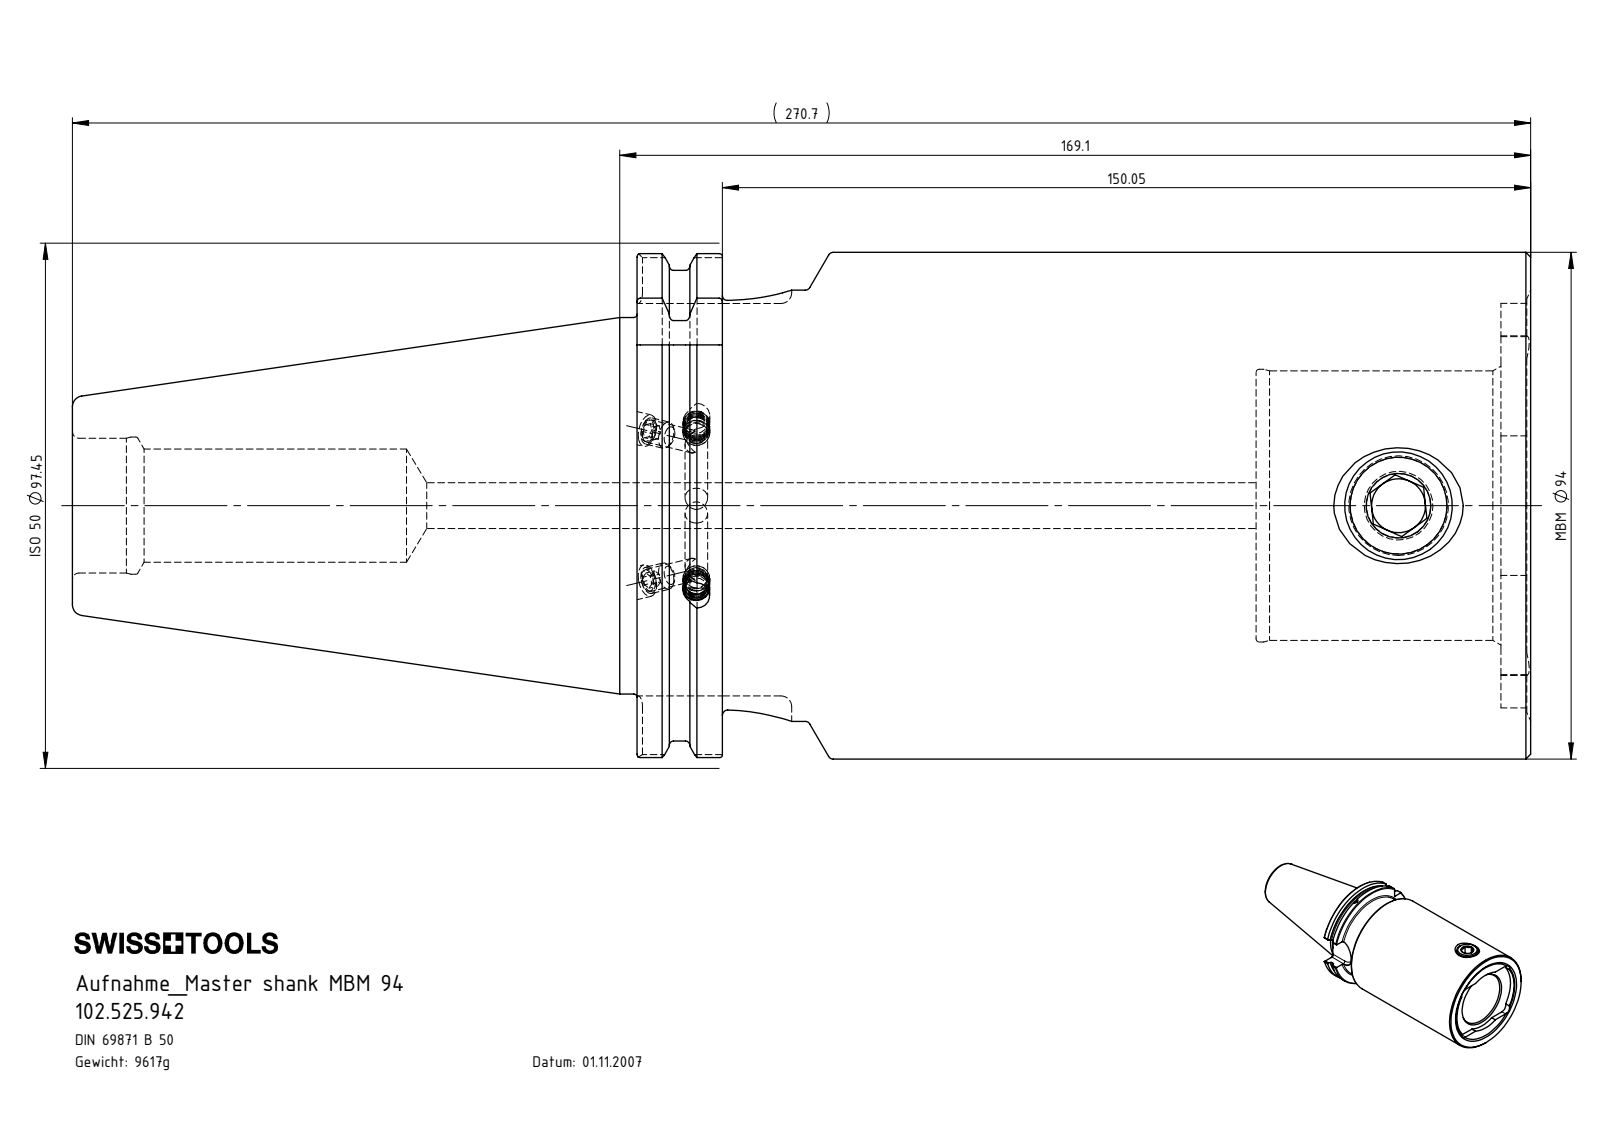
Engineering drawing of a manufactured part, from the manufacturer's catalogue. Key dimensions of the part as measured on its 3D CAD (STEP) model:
Part name (STEP PRODUCT): 102.525.942; SB5-MB9.K01.169_D_mit Bundkhlung; KVT_MB_600_050; MB9-ER1.001.032_A (+1 more)
STEP written by: SolidWorks 2017 (CONFIG_CONTROL_DESIGN)
Units: millimetres
Bodies: 8 solids, 313 faces (80 planar, 88 cylindrical, 145 other)
Overall size (bounding box): 270.7 × 97.45 × 94
Volume: 1 225 000 mm³ · Surface area: 103 842 mm²
Round holes (diameter × count): ⌀4.2 ×3, ⌀4 ×2, ⌀6 ×2, ⌀5 ×1, ⌀8.5 ×1, ⌀10 ×1, ⌀18.5 ×1, ⌀21 ×1, ⌀25 ×1, ⌀25.45 ×1, ⌀50 ×1, ⌀50.6 ×1
Round bosses / shafts (diameter × count): ⌀5 ×3, ⌀94 ×1, ⌀91 ×1, ⌀80 ×1, ⌀69.85 ×1, ⌀20 ×1
Partial cylindrical surfaces — rounded edges, fillets, slot ends (radius × count): R2 ×8, R5.2 ×4, R12.85 ×1, R30 ×1, R37.52 ×1, R48.73 ×1
Main face-to-face distances: 114.9, 160.35, 45.45, 165.9, 51, 5.55, 15.85, 99.05, 144.5, 150.05
